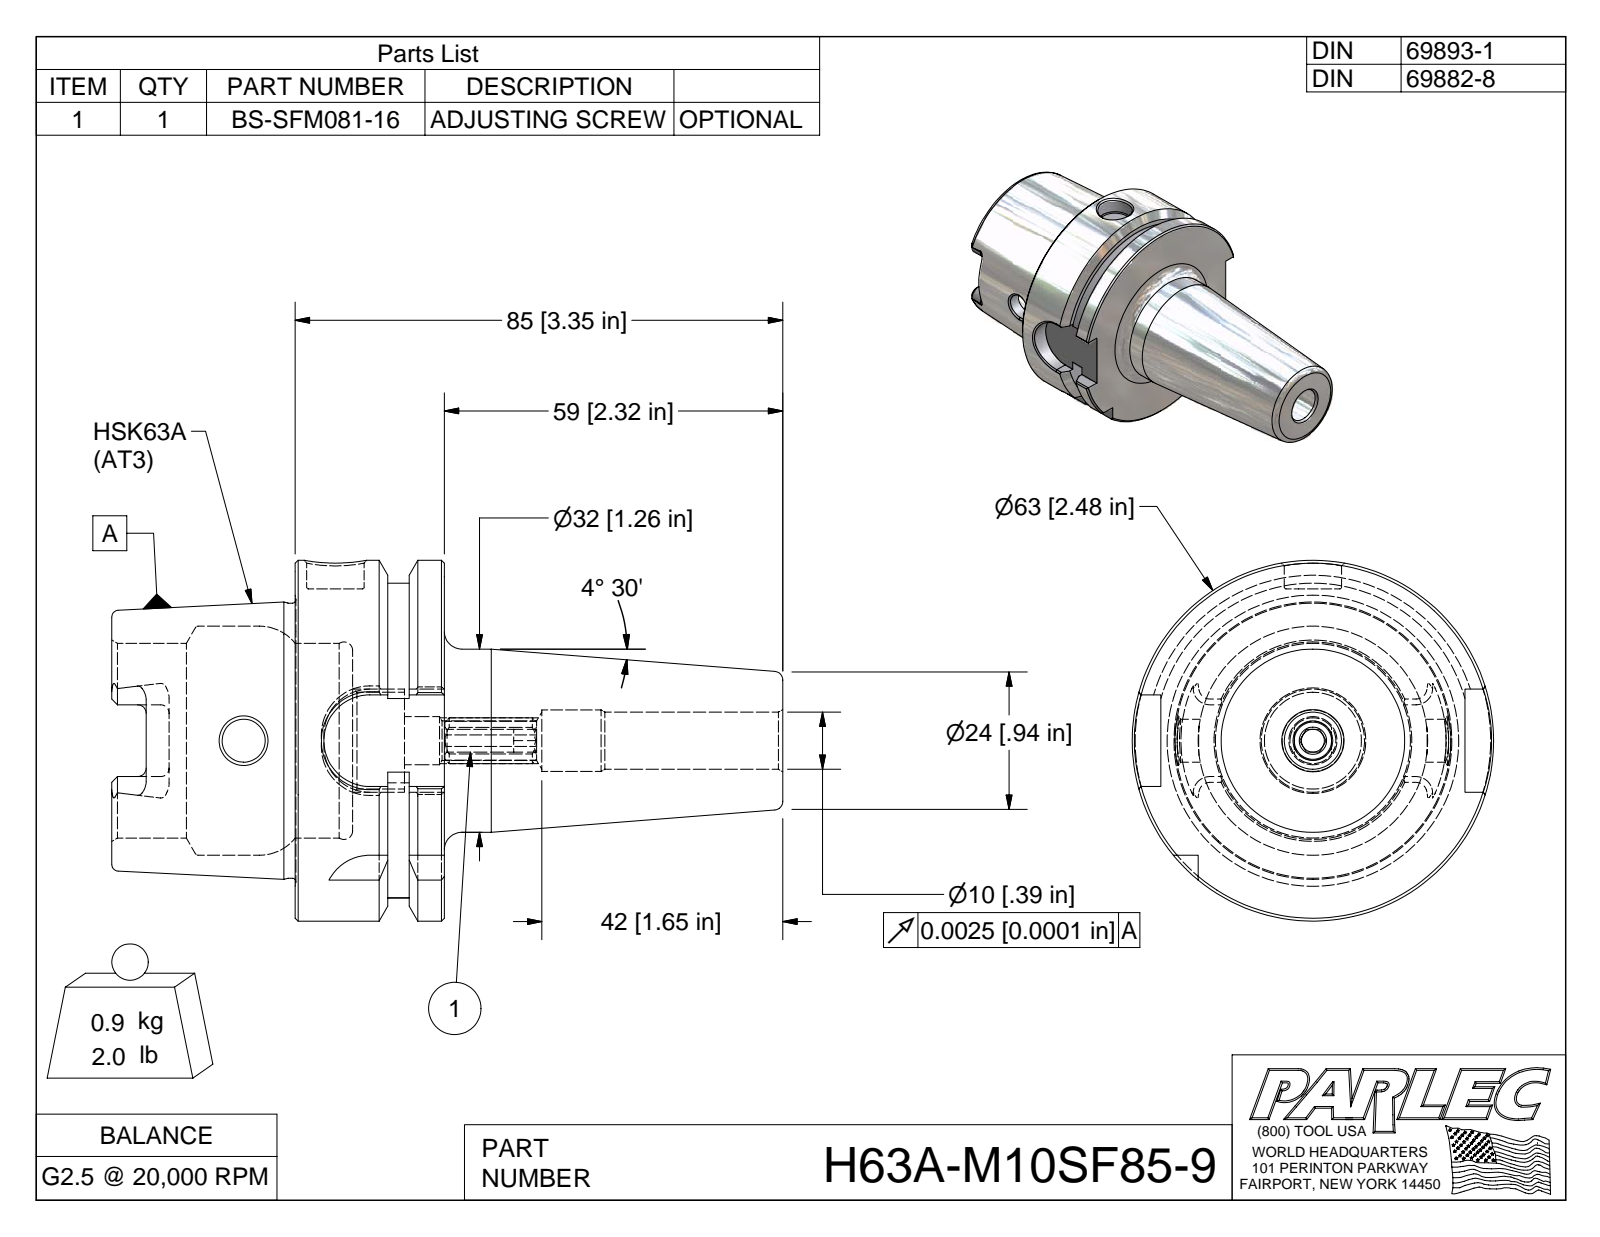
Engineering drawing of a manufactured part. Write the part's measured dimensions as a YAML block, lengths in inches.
part_name: "H63A-M10SF85-9; H63A-M10SF85-9-1; BS-SFM081-16"
step_written_by: "Autodesk Inventor 2009 (AUTOMOTIVE_DESIGN)"
units: inches
bodies: {solids: 2, faces: 157, planar: 58, cylindrical: 35, other: 64}
overall_size: [4.606, 2.48, 2.48]
volume: 7.103
surface_area: 45.65
round_holes:
  - {diameter: 0.295, count: 1}
  - {diameter: 0.393, count: 1}
  - {diameter: 0.394, count: 1}
  - {diameter: 0.423, count: 1}
  - {diameter: 0.666, count: 1}
  - {diameter: 1.339, count: 1}
  - {diameter: 1.575, count: 1}
round_bosses_or_shafts:
  - {diameter: 2.48, count: 1}
  - {diameter: 1.891, count: 1}
  - {diameter: 1.26, count: 1}
partial_cylinders:
  - {radius: 0.059, count: 6}
  - {radius: 0.113, count: 4}
  - {radius: 0.315, count: 4}
  - {radius: 0.157, count: 1}
  - {radius: 1.083, count: 1}
face_to_face_distances: [1.024, 0.241, 0.389, 0.394, 0.63, 1.26, 1.654, 2.283, 1.894, 0.635]
